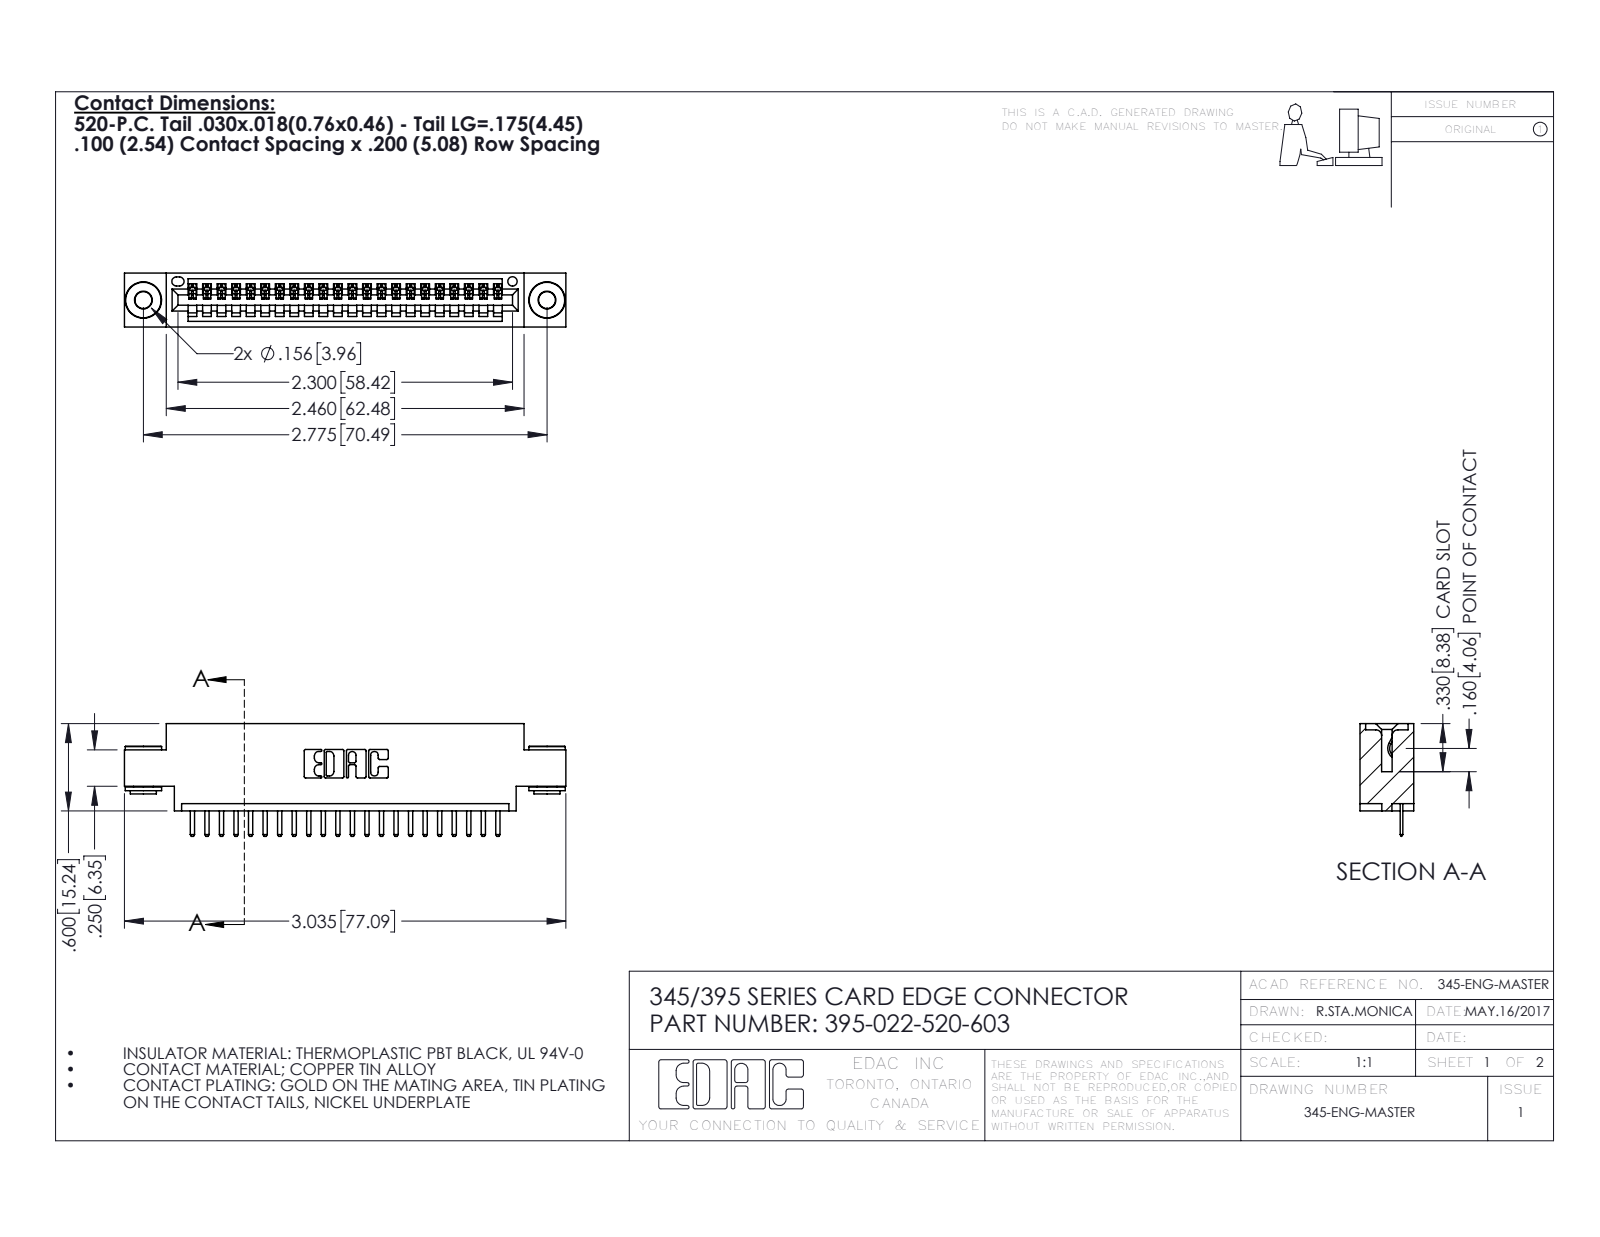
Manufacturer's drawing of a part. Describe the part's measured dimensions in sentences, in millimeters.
The part is named "345-292-001_345-293-120; 395-022-520-603; 345-250-002_345-250-002-102; 345 Part_0.170 Offset - 0.156 Dia-TH". Its 3-D file was written by "SolidWorks 2016 (CONFIG_CONTROL_DESIGN)". It is 25 solids with 1532 faces: 1018 planar, 506 cylindrical and 8 other. Overall it measures 77.1 by 19.7 by 9.4 millimeters. Its volume is 7 000 cubic millimeters and its surface area 9 168 square millimeters. Round holes: 2 of diameter 2.9, 2 of diameter 4, 1 of diameter 1.6. Round bosses or shafts: 2 of diameter 6.4, 2 of diameter 4.6, 2 of diameter 3.5. Partial cylindrical surfaces (rounded edges, fillets, slot ends): 46 of radius 0.3, 44 of radius 0.2, 22 of radius 0.3, 6 of radius 0.2, 6 of radius 0.8, 3 of radius 0.7, 2 of radius 0.8, 2 of radius 1. The main face-to-face distances are 9.4, 1.8, 7.6, 5.1, 2.5, 6.9, 0.6, 5.7, 4.4, 2.5. The hole center spacings are 6.9, 64.5, 70.5.
